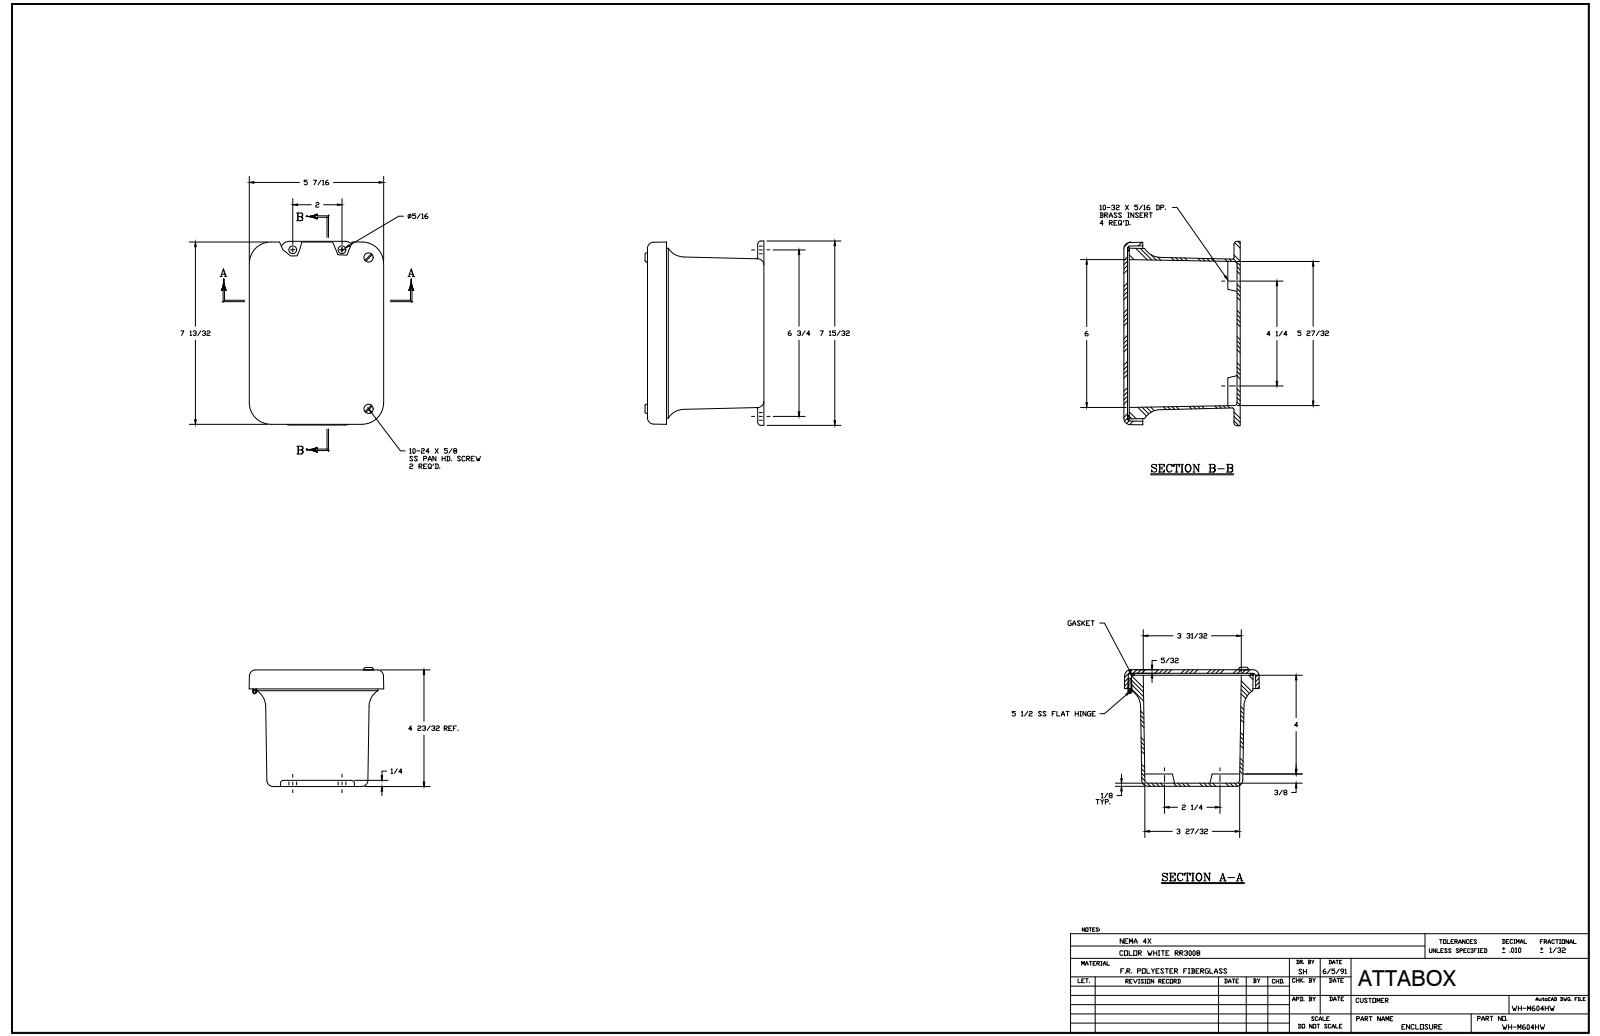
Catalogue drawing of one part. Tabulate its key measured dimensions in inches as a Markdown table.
| quantity | value |
| --- | --- |
| part name | WH-M604HW |
| STEP written by | SolidWorks 2018 (AUTOMOTIVE_DESIGN) |
| units | inches |
| bodies | 19 solids, 645 faces (200 planar, 243 cylindrical, 202 other) |
| overall size | 7.474 × 5.484 × 4.849 |
| volume | 31.3 in³ |
| surface area | 393.2 in² |
| round holes (diameter × count) | 0.131 × 5, 0.14 × 5, 0.152 × 5, 0.156 × 4, 0.218 × 4, 0.145 × 2, 0.085 × 1 |
| round bosses / shafts (diameter × count) | 0.27 × 6, 0.25 × 5, 0.125 × 4, 0.19 × 2, 0.156 × 2, 0.155 × 1, 0.125 × 1, 0.085 × 1 |
| partial cylindrical surfaces (radius × count) | 0.031 × 20, 0.125 × 12, 0.25 × 8, 0.2 × 4, 0.375 × 4, 0.75 × 4, 0.063 × 2 |
| main face-to-face distances | 0.145, 4.573, 4.718, 0.125, 4.448, 4.593, 4.5, 0.218, 4.375, 0.073 |
| hole center spacings | 2.5, 3.339, 0.5, 1.341, 2, 2.25, 4, 4.156 |
